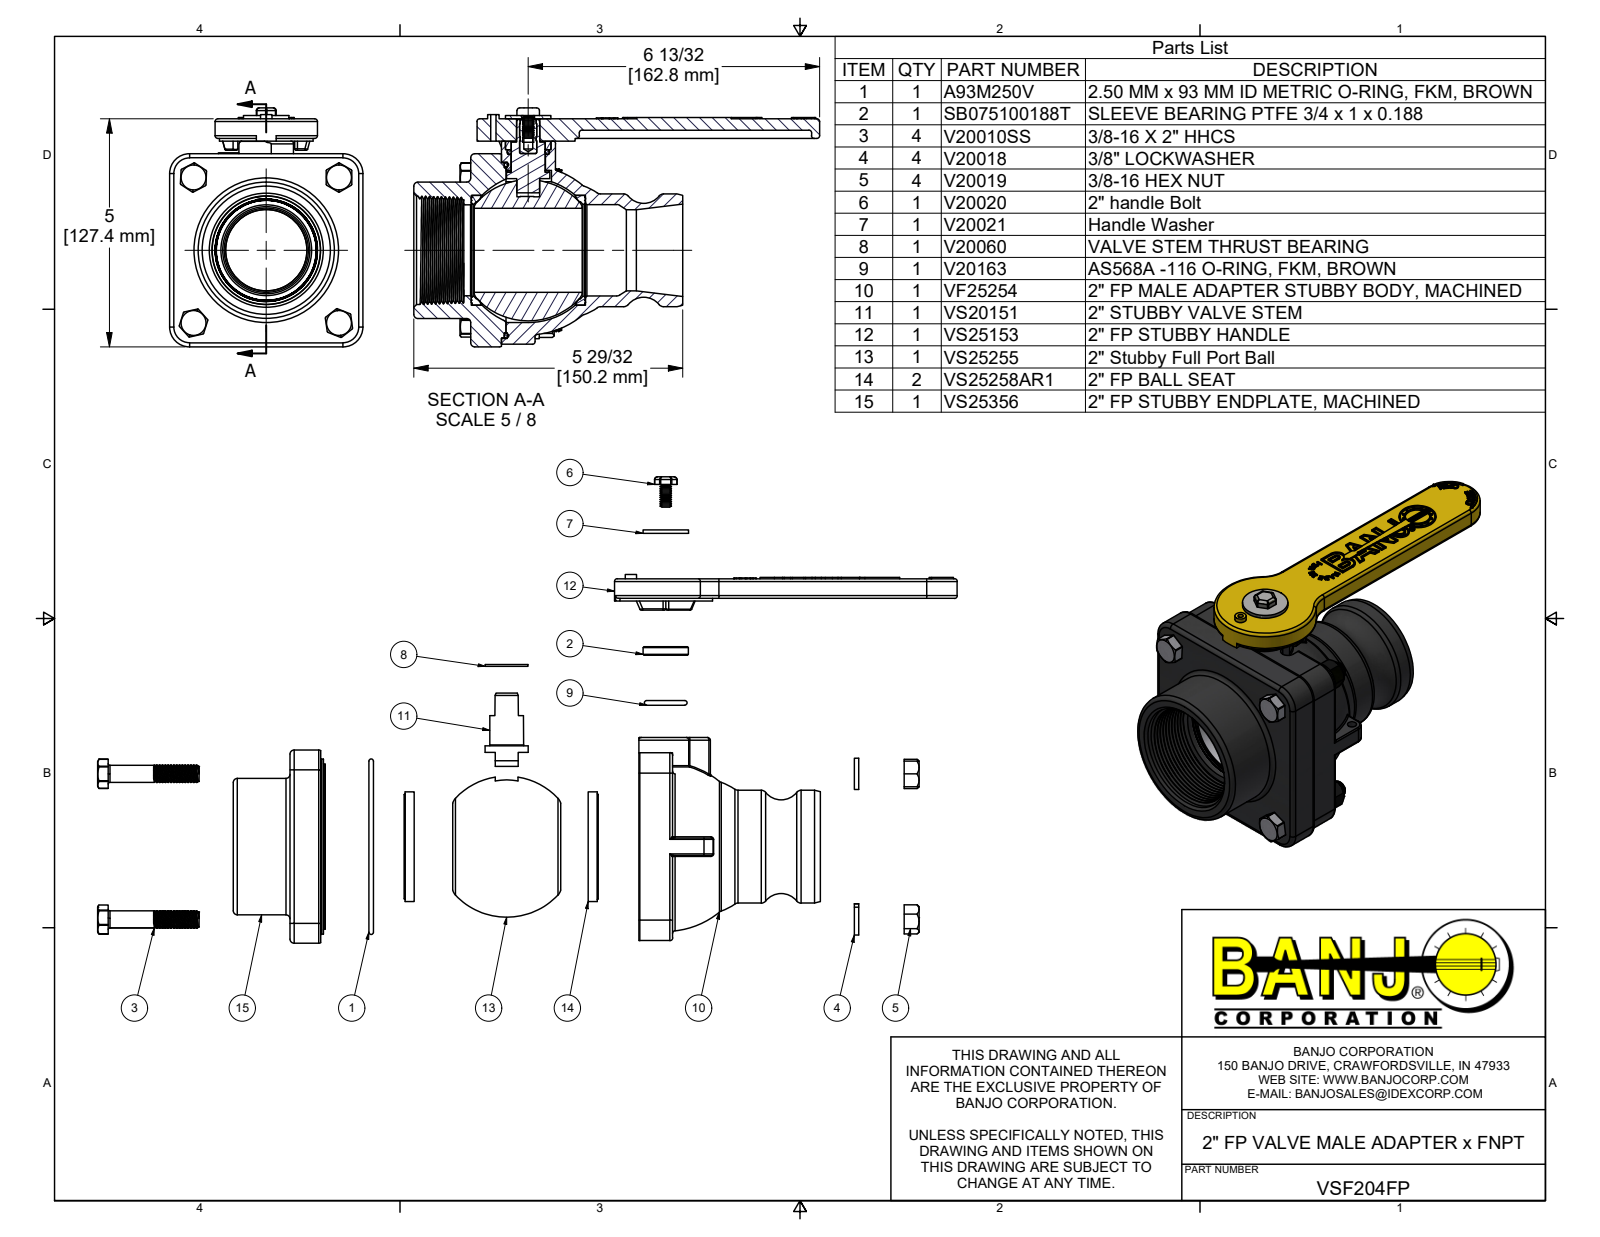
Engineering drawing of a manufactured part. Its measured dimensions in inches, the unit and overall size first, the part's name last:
Units: inches
Overall size (bounding box): 8.925 × 5.256 × 4.25
Round holes (diameter × count): ⌀0.307 ×4, ⌀0.385 ×4, ⌀0.438 ×4, ⌀0.455 ×4, ⌀0.2 ×2, ⌀0.089 ×1, ⌀0.118 ×1, ⌀0.196 ×1, ⌀0.281 ×1, ⌀0.351 ×1, ⌀0.375 ×1, ⌀0.544 ×1
Round bosses / shafts (diameter × count): ⌀0.324 ×60, ⌀0.687 ×4, ⌀0.375 ×4, ⌀3.85 ×1, ⌀3.625 ×1, ⌀3 ×1, ⌀2.481 ×1, ⌀2.412 ×1
Partial cylindrical surfaces — rounded edges, fillets, slot ends (radius × count): R0.06 ×31, R0.03 ×22, R0.09 ×8, R0.162 ×8, R0.32 ×4, R0.437 ×4, R0.45 ×4, R0.2 ×3
Main face-to-face distances: 0.675, 0.06, 0.1, 4.19, 0.775, 0.25, 1.415, 0.74, 0.64, 4.13
Hole centre spacings: 2.263, 3.2, 2.041, 2.457, 4.321, 4.526, 0.489, 0.766
Volume: 39.04 in³ · Surface area: 295.8 in²
Bodies: 26 solids, 1900 faces (614 planar, 567 cylindrical, 719 other)
Part name (STEP PRODUCT): VSF204FP; VF25254; VF25254X; VS25356 (+8 more)
STEP written by: Autodesk Inventor 2022 (AUTOMOTIVE_DESIGN)
